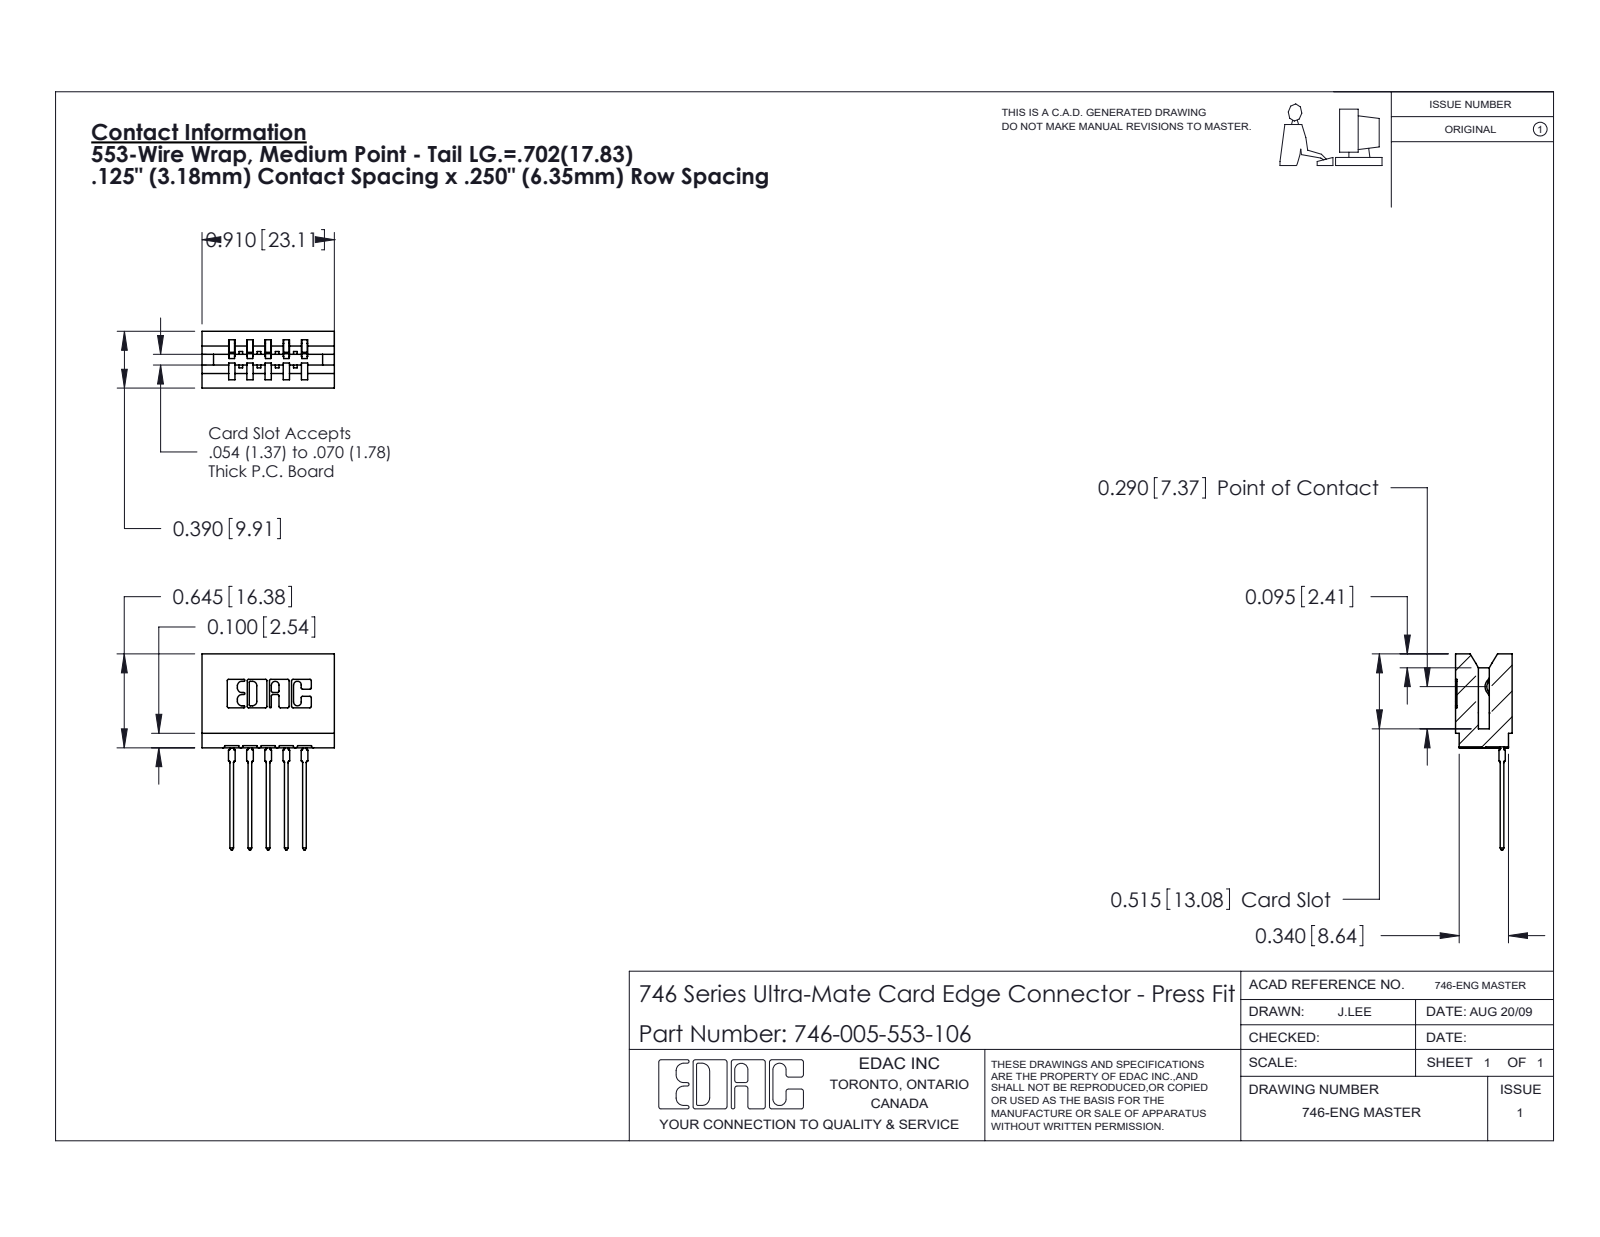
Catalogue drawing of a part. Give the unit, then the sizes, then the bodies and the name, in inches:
Units: inches
Overall size (bounding box): 1.346 × 0.91 × 0.39
Partial cylindrical surfaces — rounded edges, fillets, slot ends (radius × count): R0.01 ×22, R0.021 ×10, R0.007 ×6, R0.015 ×6, R0.031 ×6, R0.005 ×4, R0.011 ×4, R0.026 ×3
Main face-to-face distances: 0.25, 0.042, 0.333, 0.057, 0.125, 0.125, 0.39, 0.083, 0.208, 0.292
Volume: 0.163 in³ · Surface area: 5.321 in²
Bodies: 6 solids, 638 faces (371 planar, 137 cylindrical, 130 other)
Part name (STEP PRODUCT): 746 Part_.515 Slot Depth - 06; 746-005-553-106; 746-292-001_553
STEP written by: SolidWorks 2020 (CONFIG_CONTROL_DESIGN)
